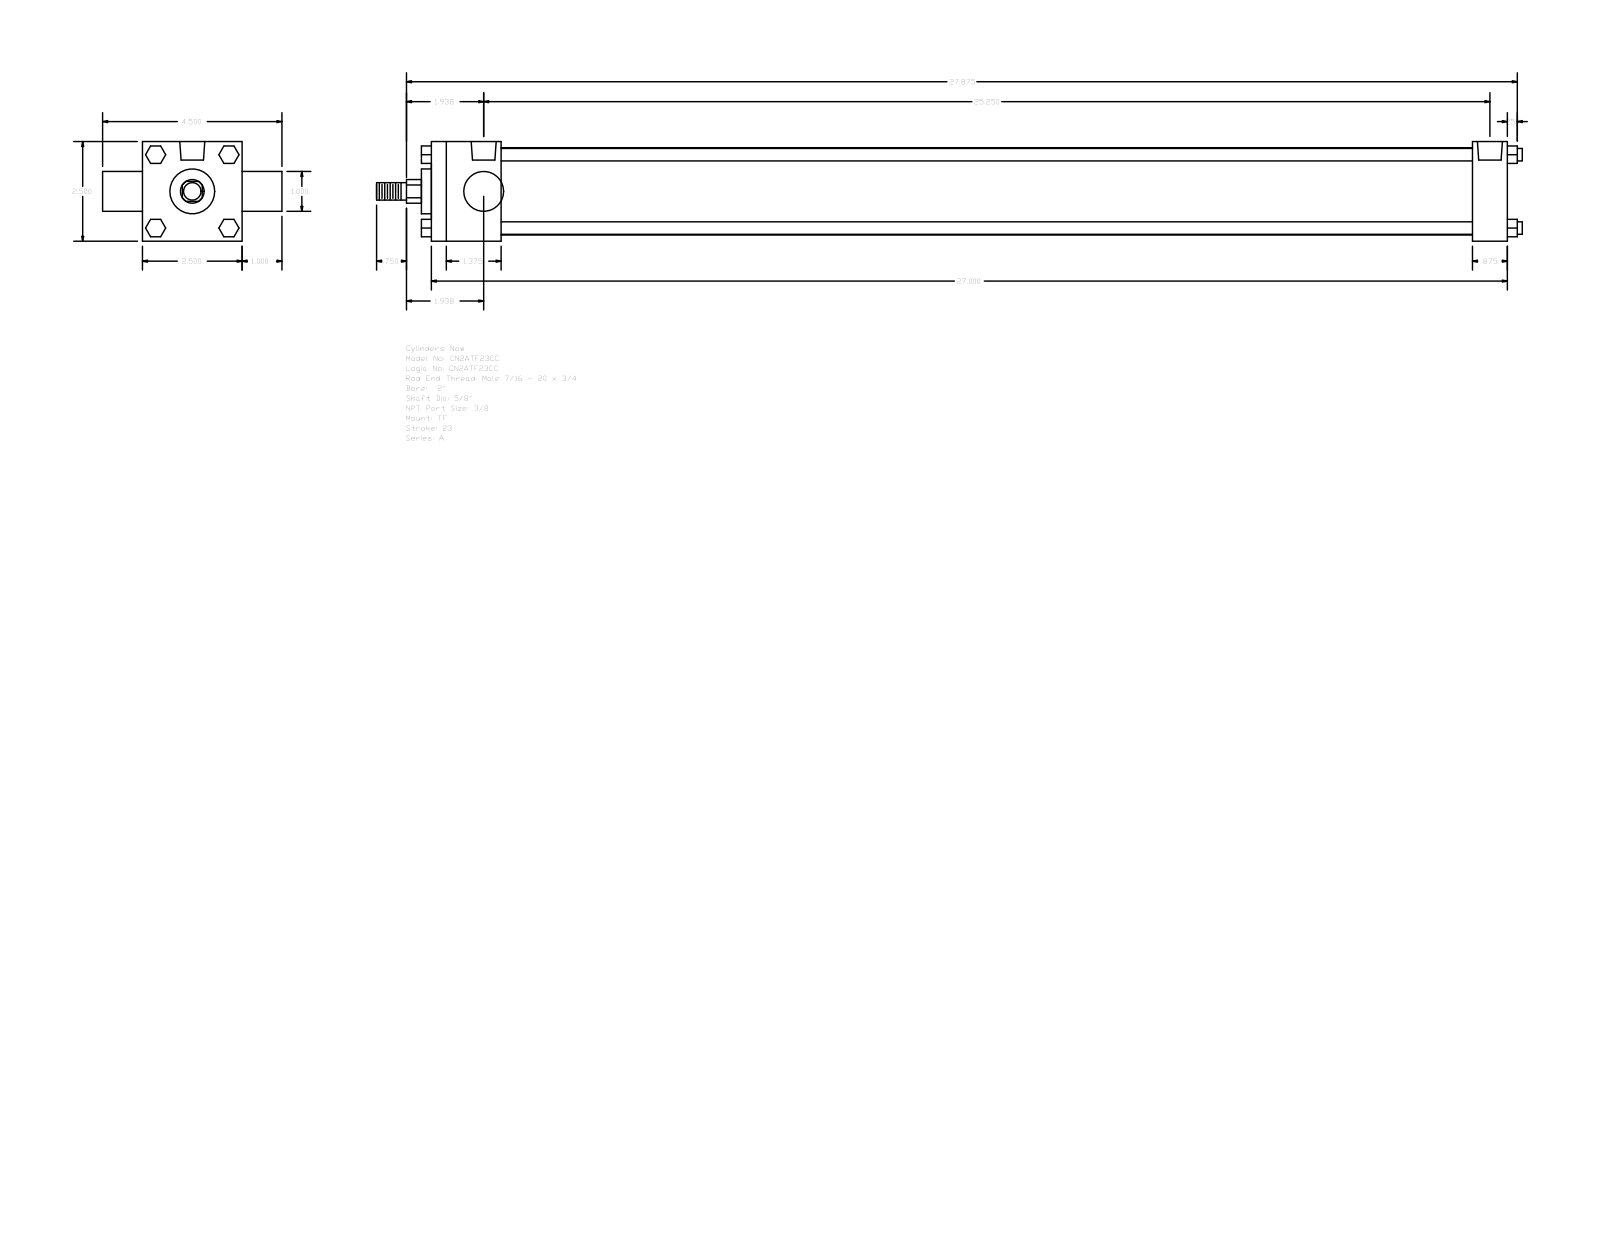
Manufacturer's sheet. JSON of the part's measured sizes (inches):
{"part_name": "A_TF__0200_0.625", "step_written_by": "GSSL Pune (CONFIG_CONTROL_DESIGN)", "units": "inches", "bodies": {"solids": 0, "faces": 120, "planar": 92, "cylindrical": 28, "other": 0}, "overall_size": [28.75, 4.5, 2.5], "round_holes": [[0.219, 3], [0.627, 2]], "round_bosses_or_shafts": [[0.313, 4], [2.19, 1], [1.125, 1], [1, 1], [0.625, 1], [0.437, 1]], "partial_cylinders_radius": [[0.297, 1]], "face_to_face_distances": [2.5, 27, 1.75, 26.125, 24.375, 25.25, 0.875, 1, 3.5, 0.25], "hole_center_spacings": [0.156, 0.157, 24.937, 25.093, 25.094, 25.25]}
